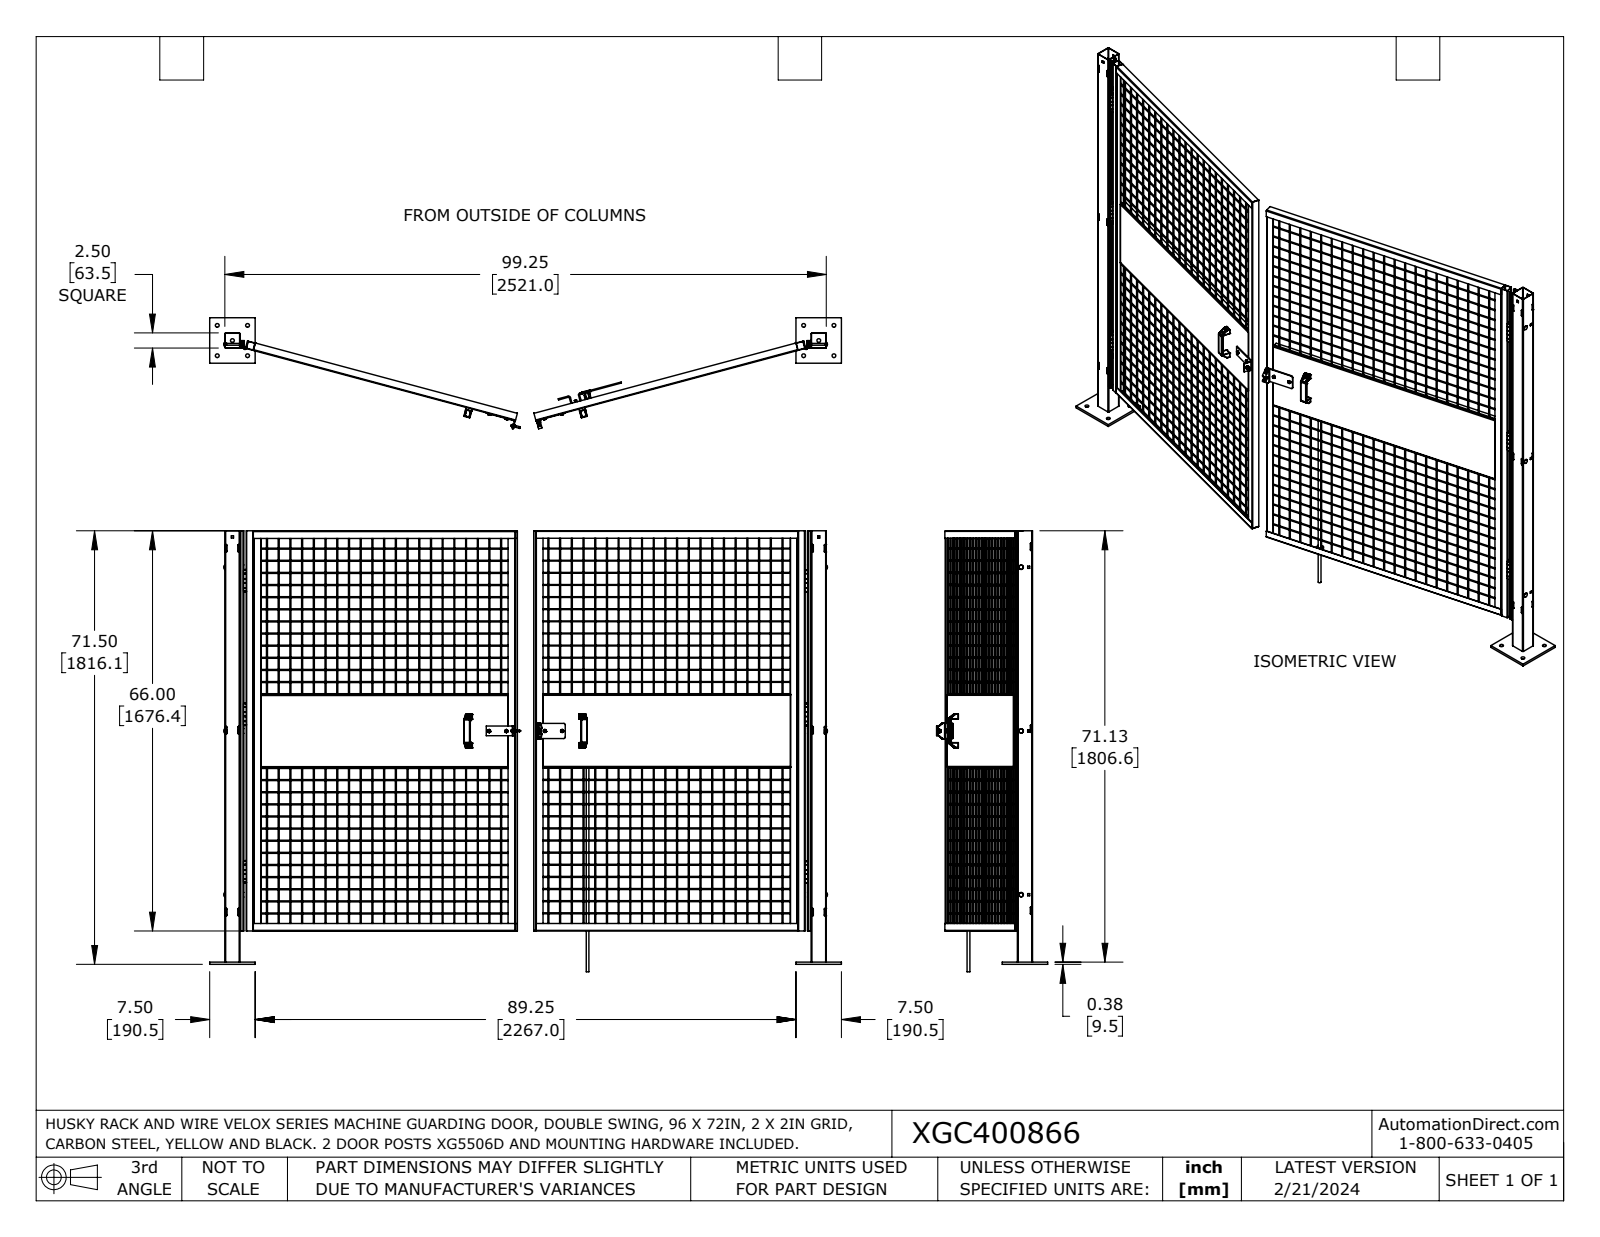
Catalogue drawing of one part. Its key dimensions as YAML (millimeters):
part_name: "XGC400866"
step_written_by: "SolidWorks 2023 (AUTOMOTIVE_DESIGN)"
units: millimeters
bodies: {solids: 87, faces: 2642, planar: 1511, cylindrical: 741, other: 390}
overall_size: [2648, 1847.5, 465.7]
volume: 7671000
surface_area: 7974000
round_holes:
  - {diameter: 9.1, count: 12}
  - {diameter: 6.4, count: 11}
  - {diameter: 15.9, count: 10}
  - {diameter: 12.7, count: 9}
  - {diameter: 4.6, count: 8}
  - {diameter: 6, count: 4}
  - {diameter: 6.1, count: 4}
  - {diameter: 3.5, count: 2}
  - {diameter: 4.3, count: 2}
  - {diameter: 4.7, count: 1}
  - {diameter: 7.4, count: 1}
  - {diameter: 9.5, count: 1}
round_bosses_or_shafts:
  - {diameter: 4.2, count: 56}
  - {diameter: 4.1, count: 46}
  - {diameter: 15.1, count: 8}
  - {diameter: 6.4, count: 8}
  - {diameter: 8.1, count: 6}
  - {diameter: 17.4, count: 4}
  - {diameter: 11.1, count: 2}
  - {diameter: 10.9, count: 2}
partial_cylinders:
  - {radius: 1.3, count: 56}
  - {radius: 0.2, count: 48}
  - {radius: 3.3, count: 31}
  - {radius: 0.6, count: 20}
  - {radius: 1.6, count: 20}
  - {radius: 3.2, count: 17}
  - {radius: 1.6, count: 16}
  - {radius: 3, count: 14}
face_to_face_distances: [1.8, 1.5, 62, 1.8, 63.5, 2457.5, 60.6, 30.2, 1.5, 0.5]
hole_center_spacings: [121.9, 122, 89.8, 127, 66.7, 173.2, 2457.5, 62.9]
